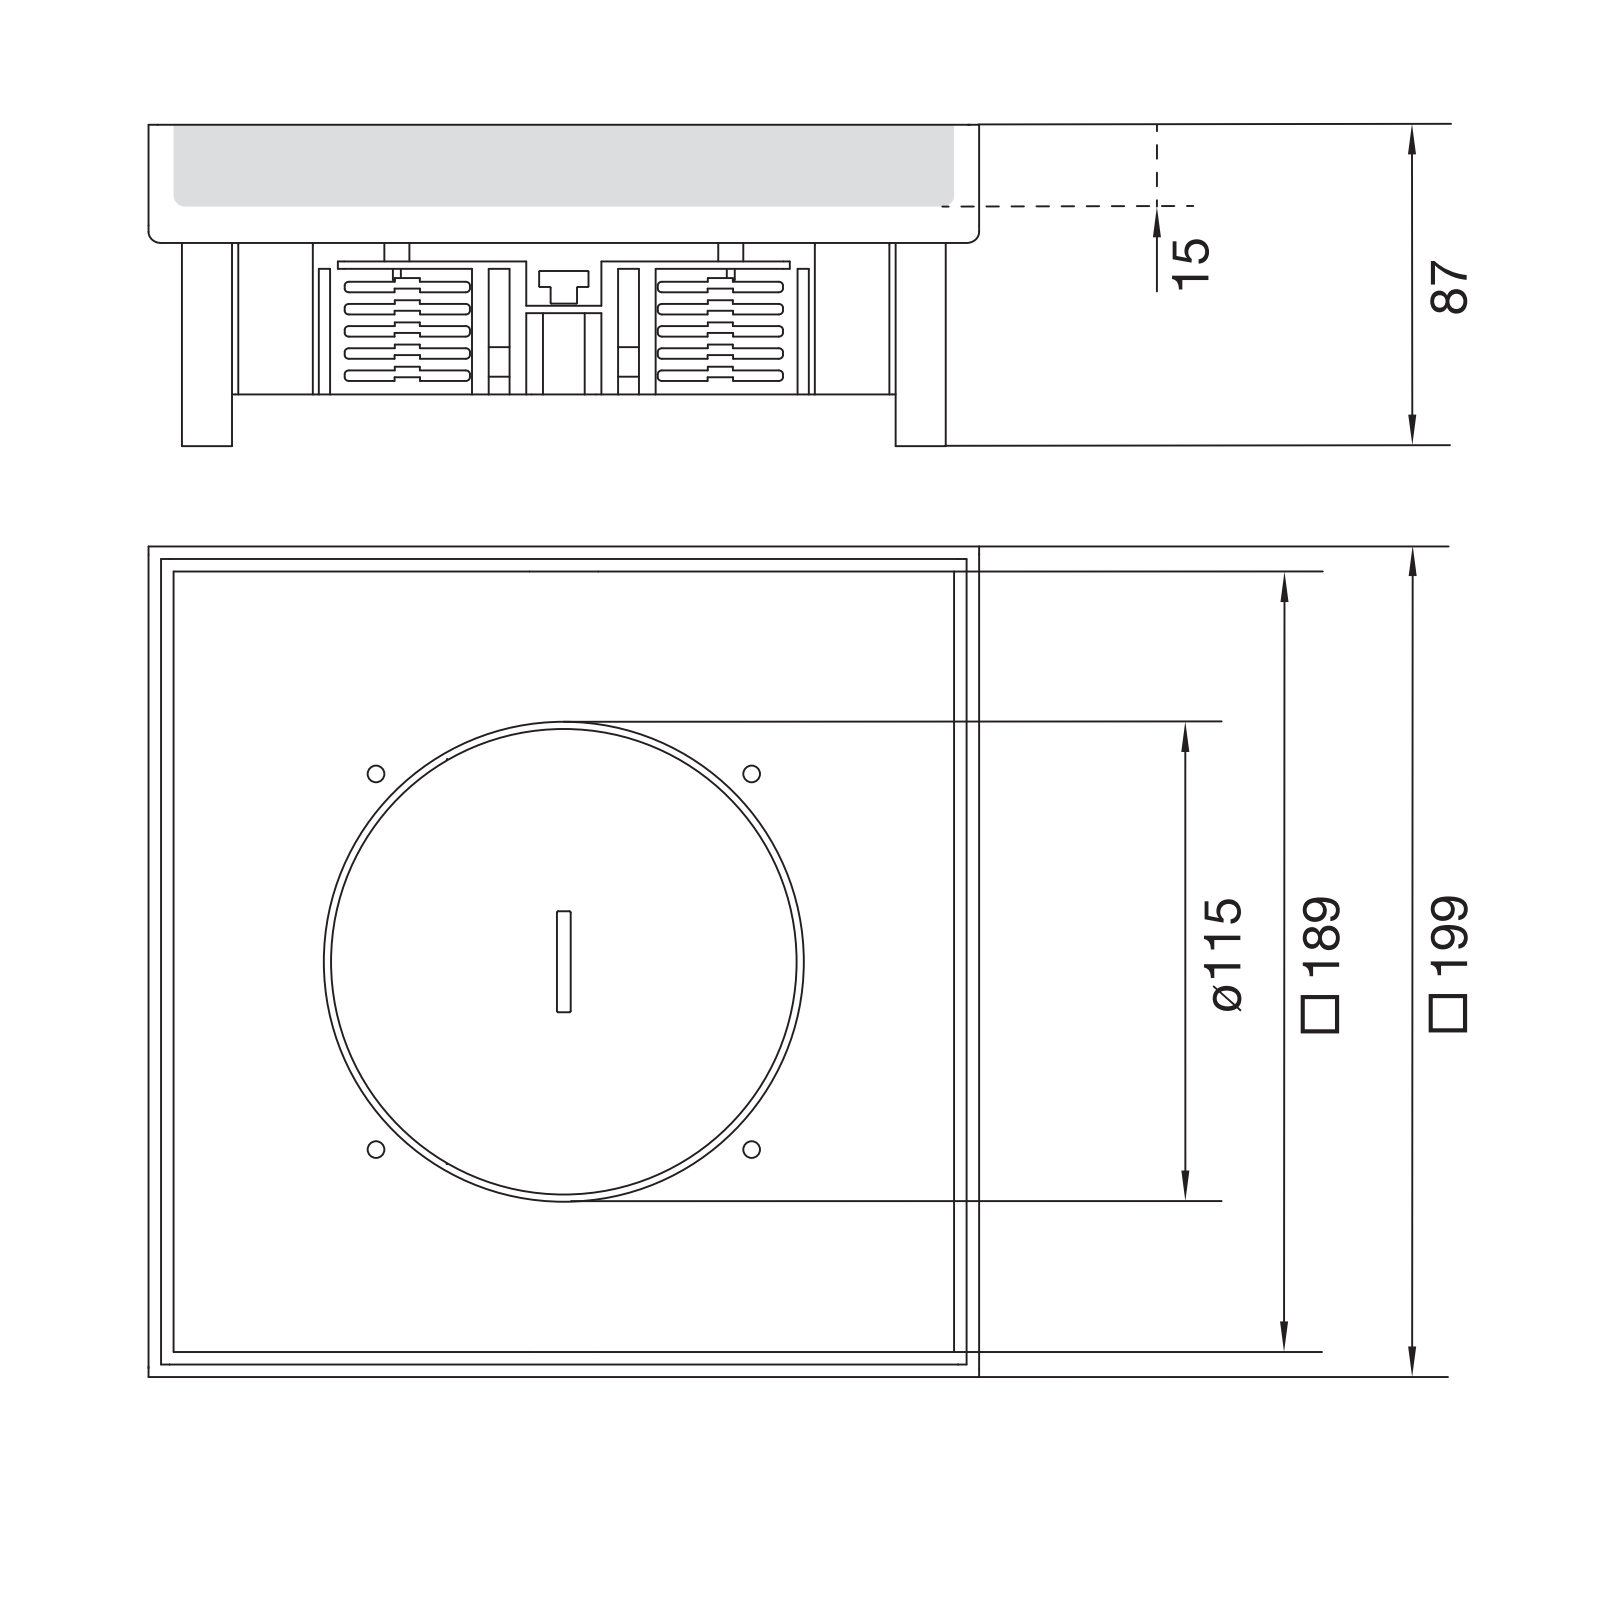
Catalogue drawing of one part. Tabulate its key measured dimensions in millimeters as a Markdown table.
| quantity | value |
| --- | --- |
| part name | T-00597; T-00595; T-00806_ASM; U09001 (+8 more) |
| STEP written by | CREO PARAMETRIC BY PTC INC, 2022024 (AUTOMOTIVE_DESIGN) |
| units | millimeters |
| bodies | 11 solids, 276 faces (155 planar, 111 cylindrical, 10 other) |
| overall size | 199 × 199 × 87 |
| volume | 559 238 mm³ |
| surface area | 350 829 mm² |
| round holes (diameter × count) | 5 × 4, 6.8 × 4, 8.5 × 4, 4.5 × 3, 80.59 × 1, 90 × 1, 101 × 1, 107 × 1, 108.6 × 1, 112 × 1, 112.4 × 1, 117 × 1 |
| round bosses / shafts (diameter × count) | 12 × 4, 9.85 × 4, 115 × 1, 111 × 1, 105 × 1, 97.6 × 1 |
| partial cylindrical surfaces (radius × count) | 1 × 8, 3 × 8, 105 × 5, 2 × 4, 5 × 3, 43 × 1, 107 × 1 |
| main face-to-face distances | 2, 15, 3, 10, 12, 17, 5, 197, 2.5, 194 |
| hole center spacings | 136.64, 57.28, 63.64, 90, 120.92, 171, 184.55, 54 |
